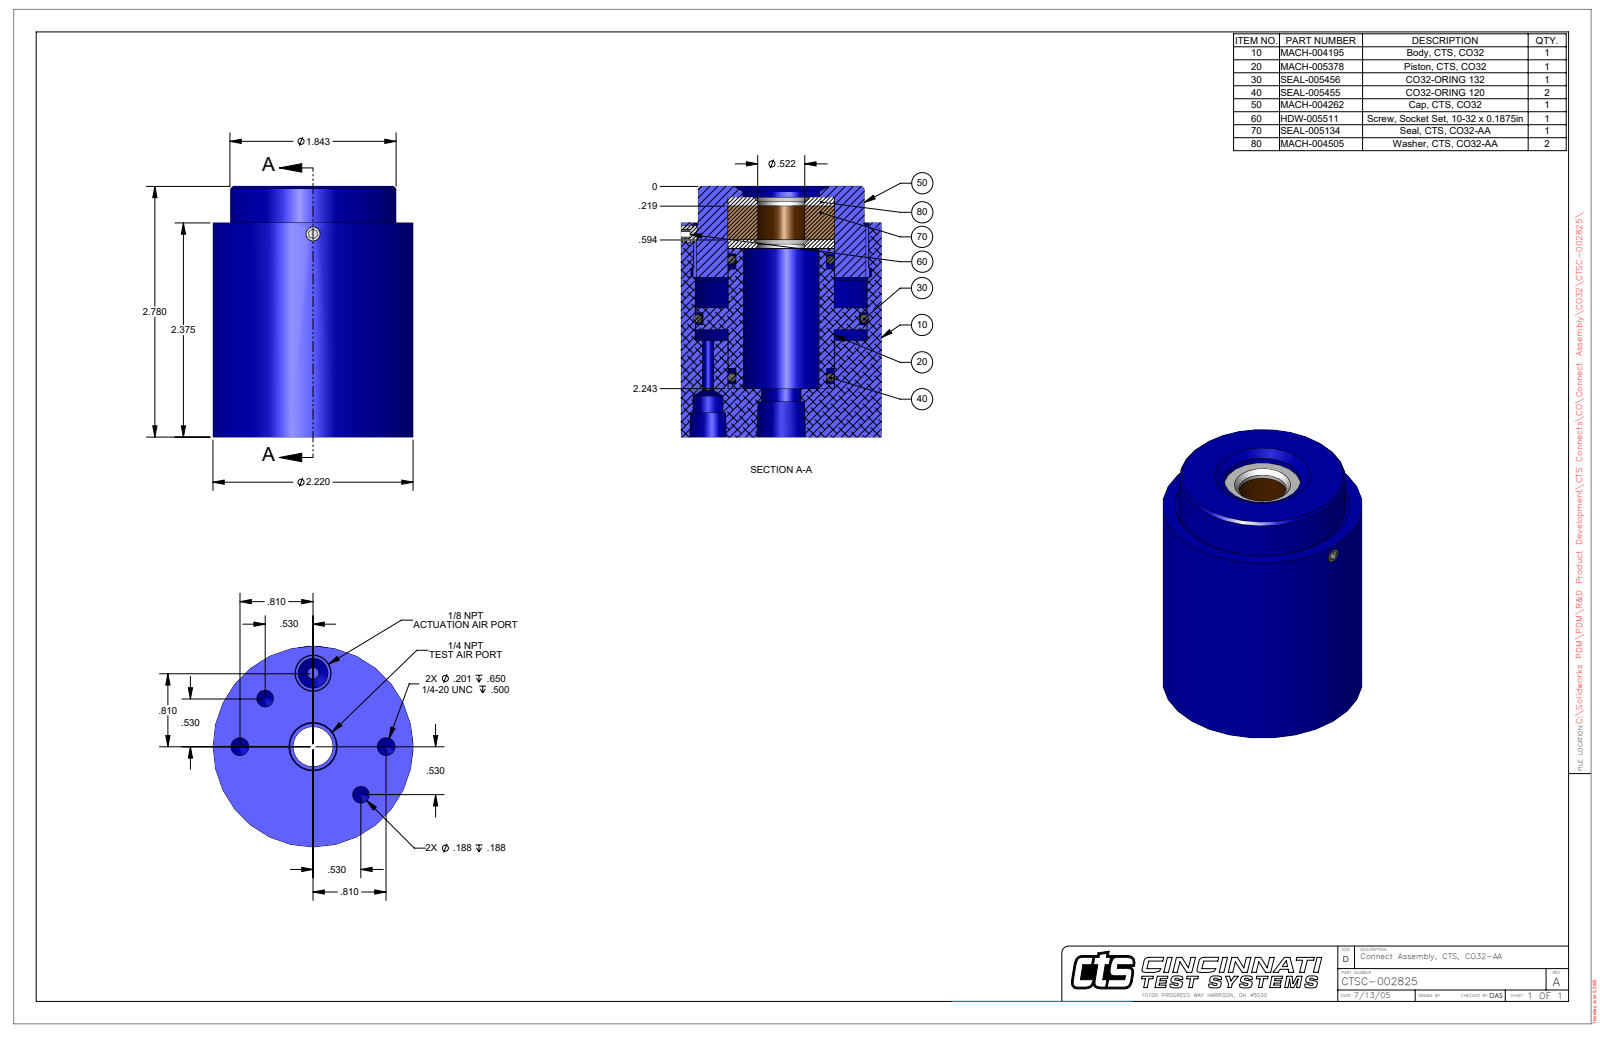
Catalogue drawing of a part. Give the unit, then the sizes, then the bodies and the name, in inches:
Units: inches
Overall size (bounding box): 2.78 × 2.22 × 2.22
Round holes (diameter × count): ⌀0.187 ×2, ⌀0.201 ×2, ⌀0.094 ×1, ⌀0.125 ×1, ⌀0.159 ×1, ⌀0.332 ×1, ⌀0.438 ×1, ⌀0.522 ×1, ⌀0.524 ×1, ⌀0.837 ×1, ⌀0.848 ×1, ⌀0.866 ×1
Round bosses / shafts (diameter × count): ⌀2.22 ×1, ⌀1.843 ×1, ⌀1.172 ×1
Partial cylindrical surfaces — rounded edges, fillets, slot ends (radius × count): R0.095 ×1, R1.092 ×1
Main face-to-face distances: 2.78, 2.375, 0.405, 0.537, 1.837, 2.243, 2.092, 1.554, 0.283, 0.688
Hole centre spacings: 0.6, 0.81, 1.441, 0.75, 1.145, 1.5, 1.62
Volume: 8.987 in³ · Surface area: 35.66 in²
Bodies: 1 solid, 124 faces (51 planar, 48 cylindrical, 25 other)
Part name (STEP PRODUCT): CTSC-002825
STEP written by: SolidWorks 2023 (AUTOMOTIVE_DESIGN)
